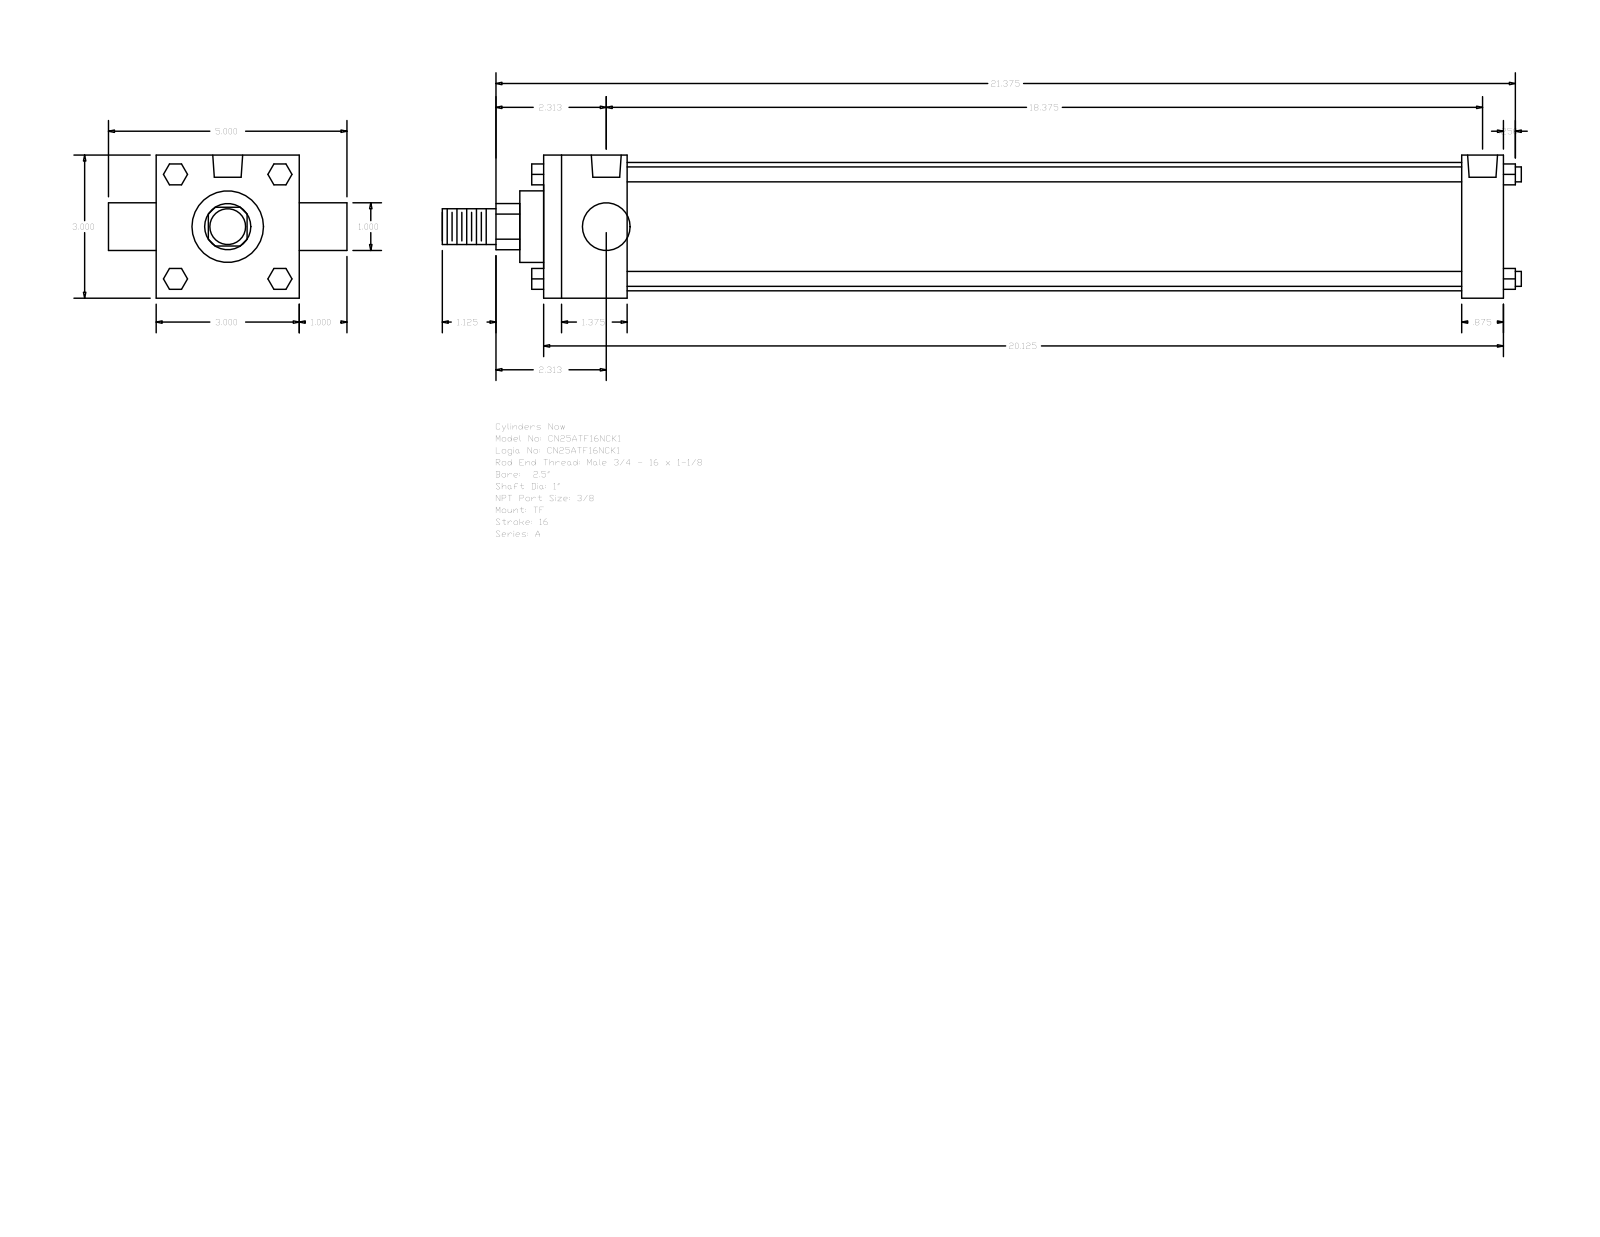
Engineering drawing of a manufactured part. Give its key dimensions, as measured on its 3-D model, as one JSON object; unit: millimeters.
{"part_name": "A_TF__0250_1", "step_written_by": "GSSL Pune (CONFIG_CONTROL_DESIGN)", "units": "millimeters", "bodies": {"solids": 0, "faces": 120, "planar": 92, "cylindrical": 28, "other": 0}, "overall_size": [574.67, 127, 76.2], "round_holes": [[5.56, 3], [15.93, 2]], "round_bosses_or_shafts": [[7.94, 4], [25.4, 2], [68.33, 1], [38.1, 1], [19.05, 1]], "partial_cylinders_radius": [[12.29, 1]], "face_to_face_distances": [76.2, 511.18, 44.45, 488.95, 444.5, 466.73, 22.23, 25.4, 101.6, 12.7], "hole_center_spacings": [2.38, 469.1, 466.72, 471.48]}
